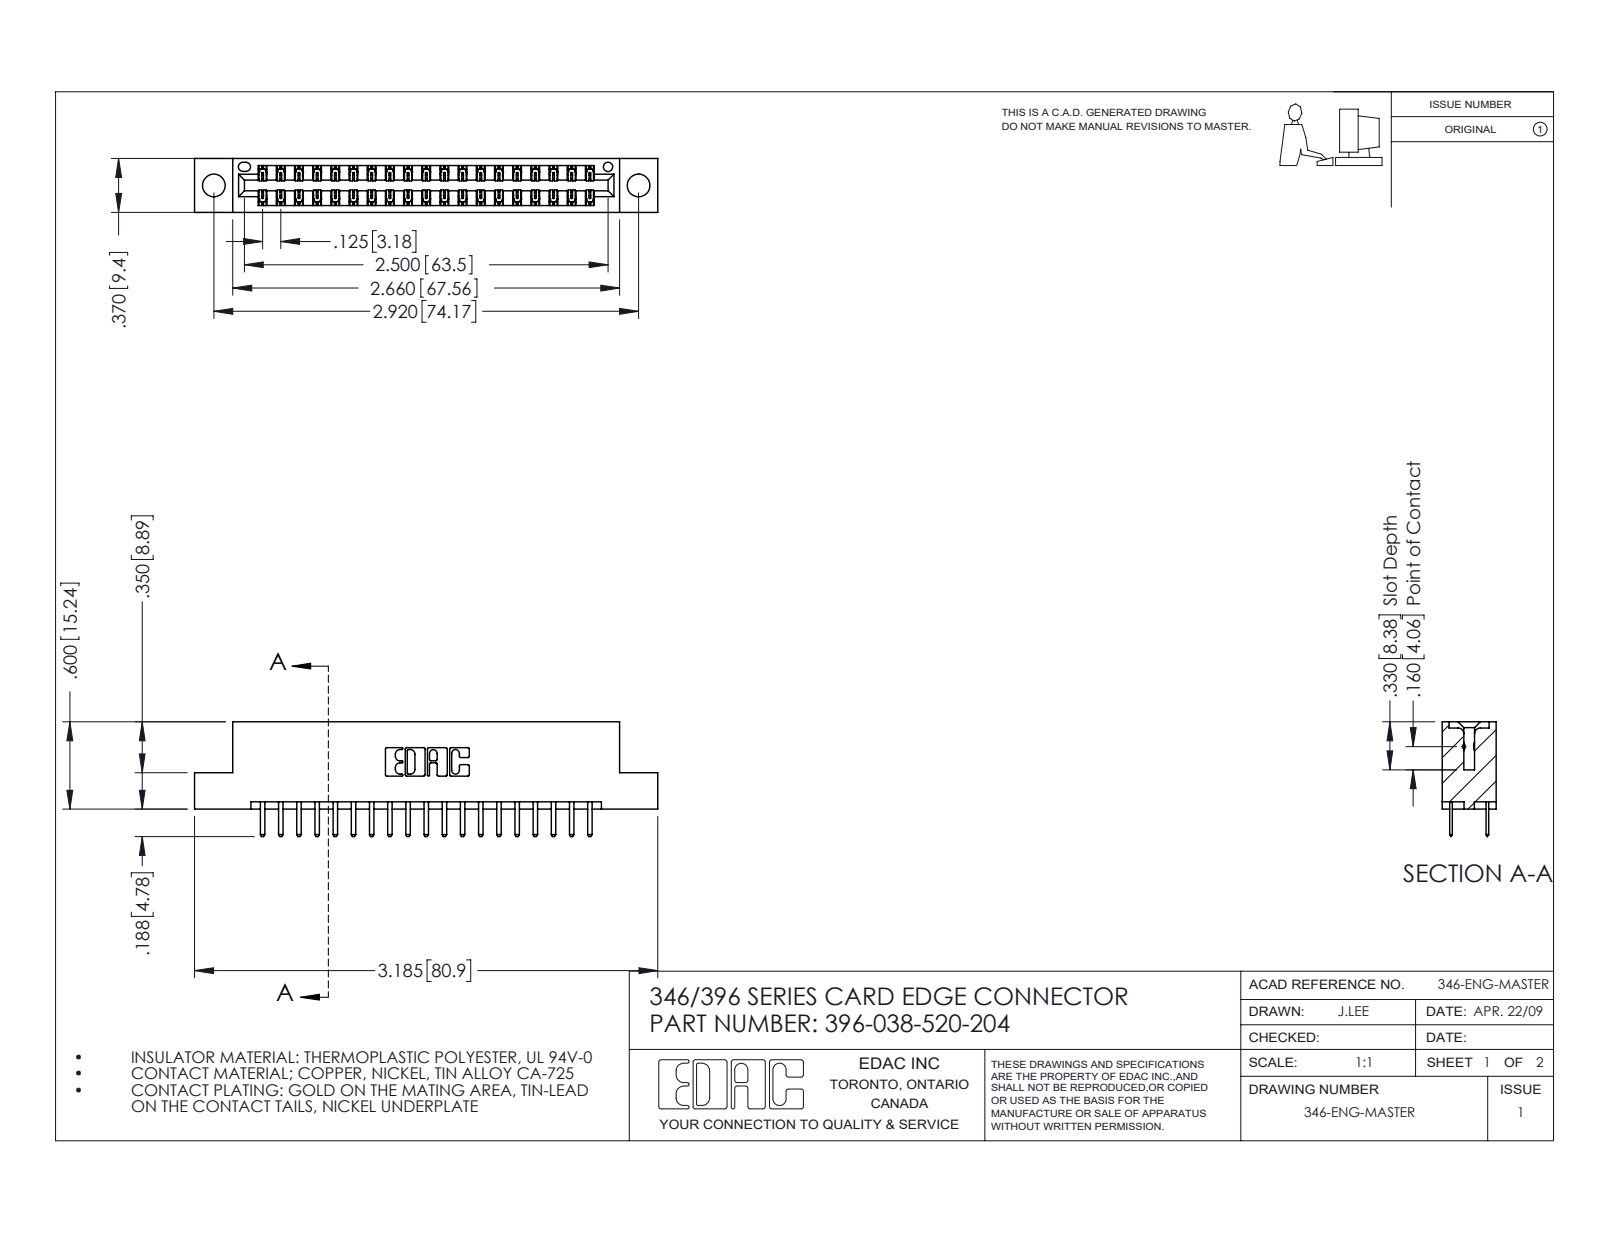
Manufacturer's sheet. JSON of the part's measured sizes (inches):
{"part_name": "346 Part_Flush Mounting Lugs - 0.156 Dia-TH; 396-038-520-204; 345-292-001_345-293-120", "step_written_by": "SolidWorks 2016 (CONFIG_CONTROL_DESIGN)", "units": "inches", "bodies": {"solids": 39, "faces": 2250, "planar": 1482, "cylindrical": 768, "other": 0}, "overall_size": [3.185, 0.788, 0.37], "volume_in3": 0.464, "surface_area_in2": 15.29, "round_holes": [[0.156, 2], [0.064, 1]], "partial_cylinders_radius": [[0.006, 57], [0.01, 42], [0.01, 22], [0.007, 6], [0.031, 6], [0.026, 3], [0.014, 2], [0.022, 2]], "face_to_face_distances": [0.048, 0.322, 0.25, 0.37, 0.275, 0.072, 0.298, 0.025, 0.148, 0.222], "hole_center_spacings": [0.246, 2.713, 2.92]}
